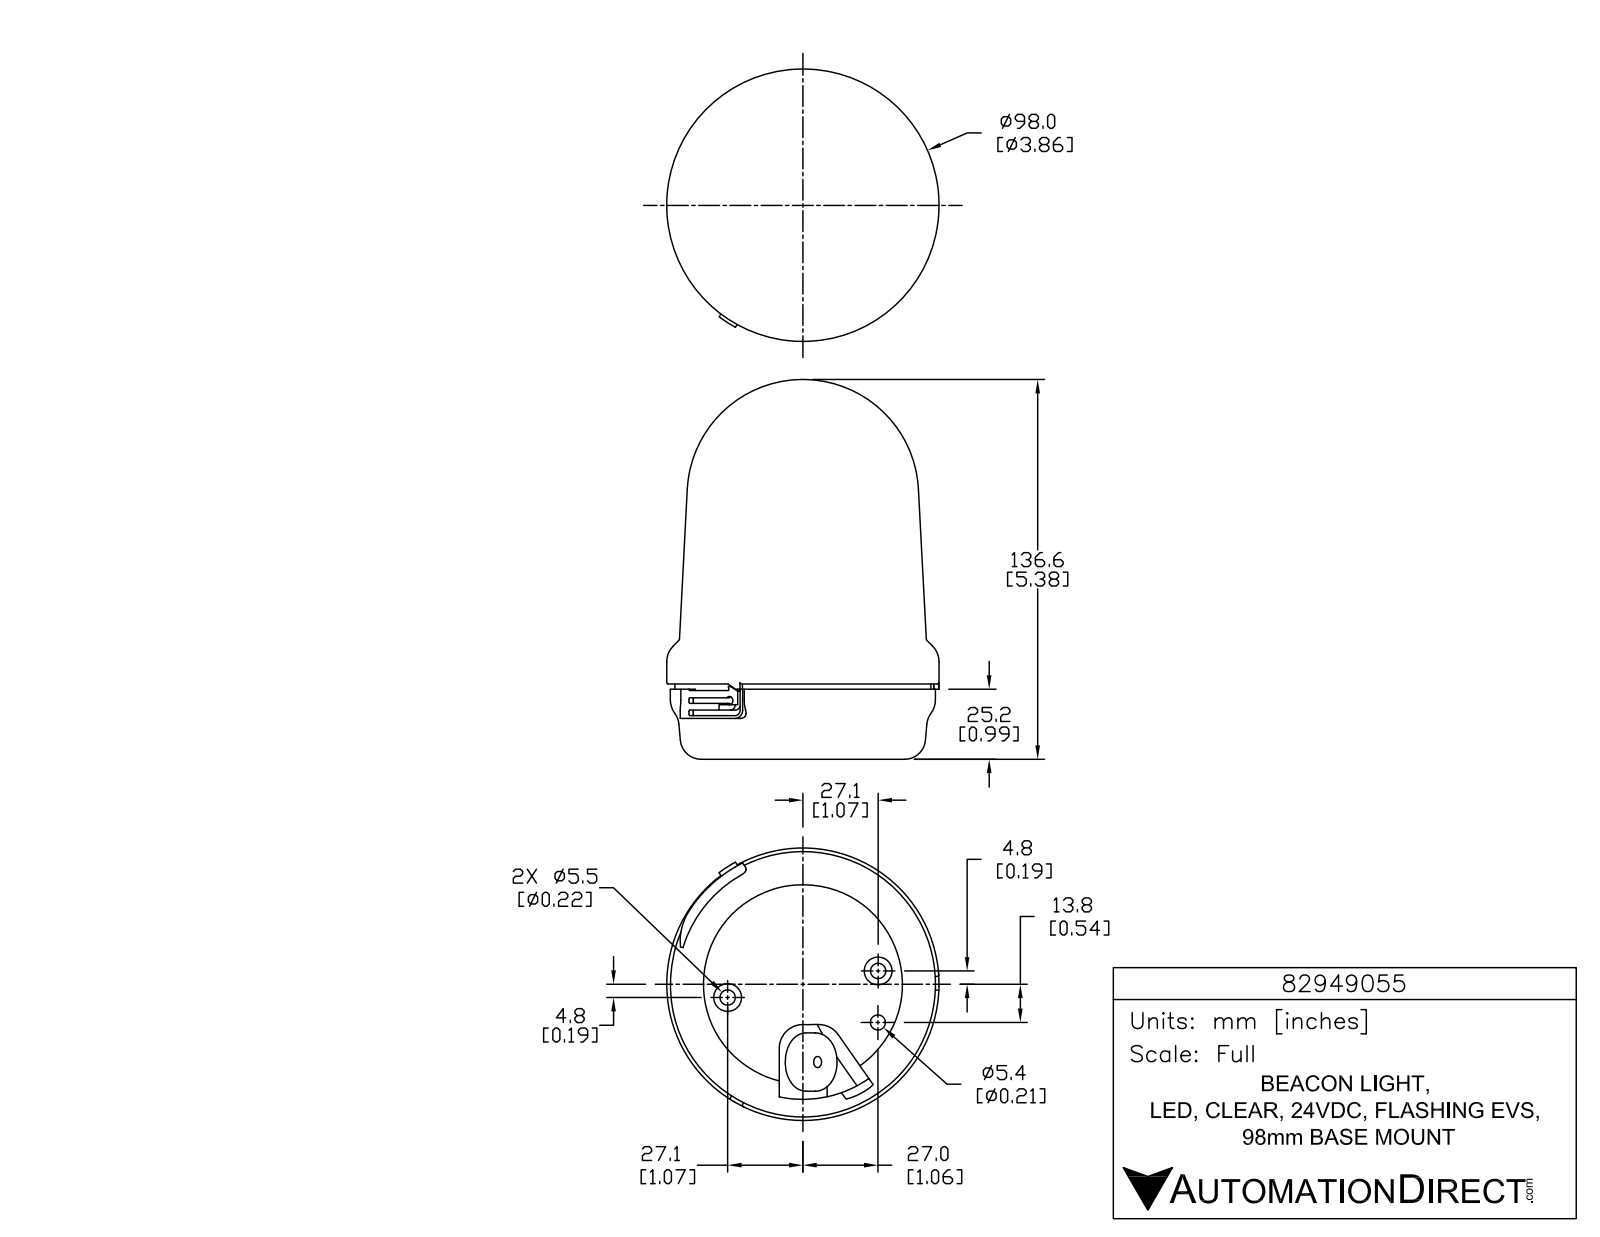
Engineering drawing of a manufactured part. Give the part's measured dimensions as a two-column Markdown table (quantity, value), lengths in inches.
| quantity | value |
| --- | --- |
| part name | 82949055 |
| STEP written by | SolidWorks 2015 (AUTOMOTIVE_DESIGN) |
| units | inches |
| bodies | 1 solid, 872 faces (566 planar, 204 cylindrical, 102 other) |
| overall size | 5.378 × 3.858 × 3.858 |
| volume | 44.69 in³ |
| surface area | 73.66 in² |
| round holes (diameter × count) | 0.059 × 3, 0.217 × 2, 0.157 × 1, 0.213 × 1, 2.819 × 1 |
| round bosses / shafts (diameter × count) | 0.339 × 3, 0.084 × 3, 0.394 × 2, 3.858 × 1, 3.756 × 1, 3.626 × 1, 0.827 × 1 |
| partial cylindrical surfaces (radius × count) | 0.005 × 9, 0.005 × 6, 0.012 × 6, 0.012 × 6, 0.012 × 6, 0.196 × 6, 0.02 × 5, 0.039 × 4 |
| main face-to-face distances | 1.045, 0.972, 0.073, 0.02, 0.992, 1.065, 0.236, 0.579, 0.559, 0.413 |
| hole center spacings | 1.083, 0.73, 1.193, 2.158, 2.165 |
